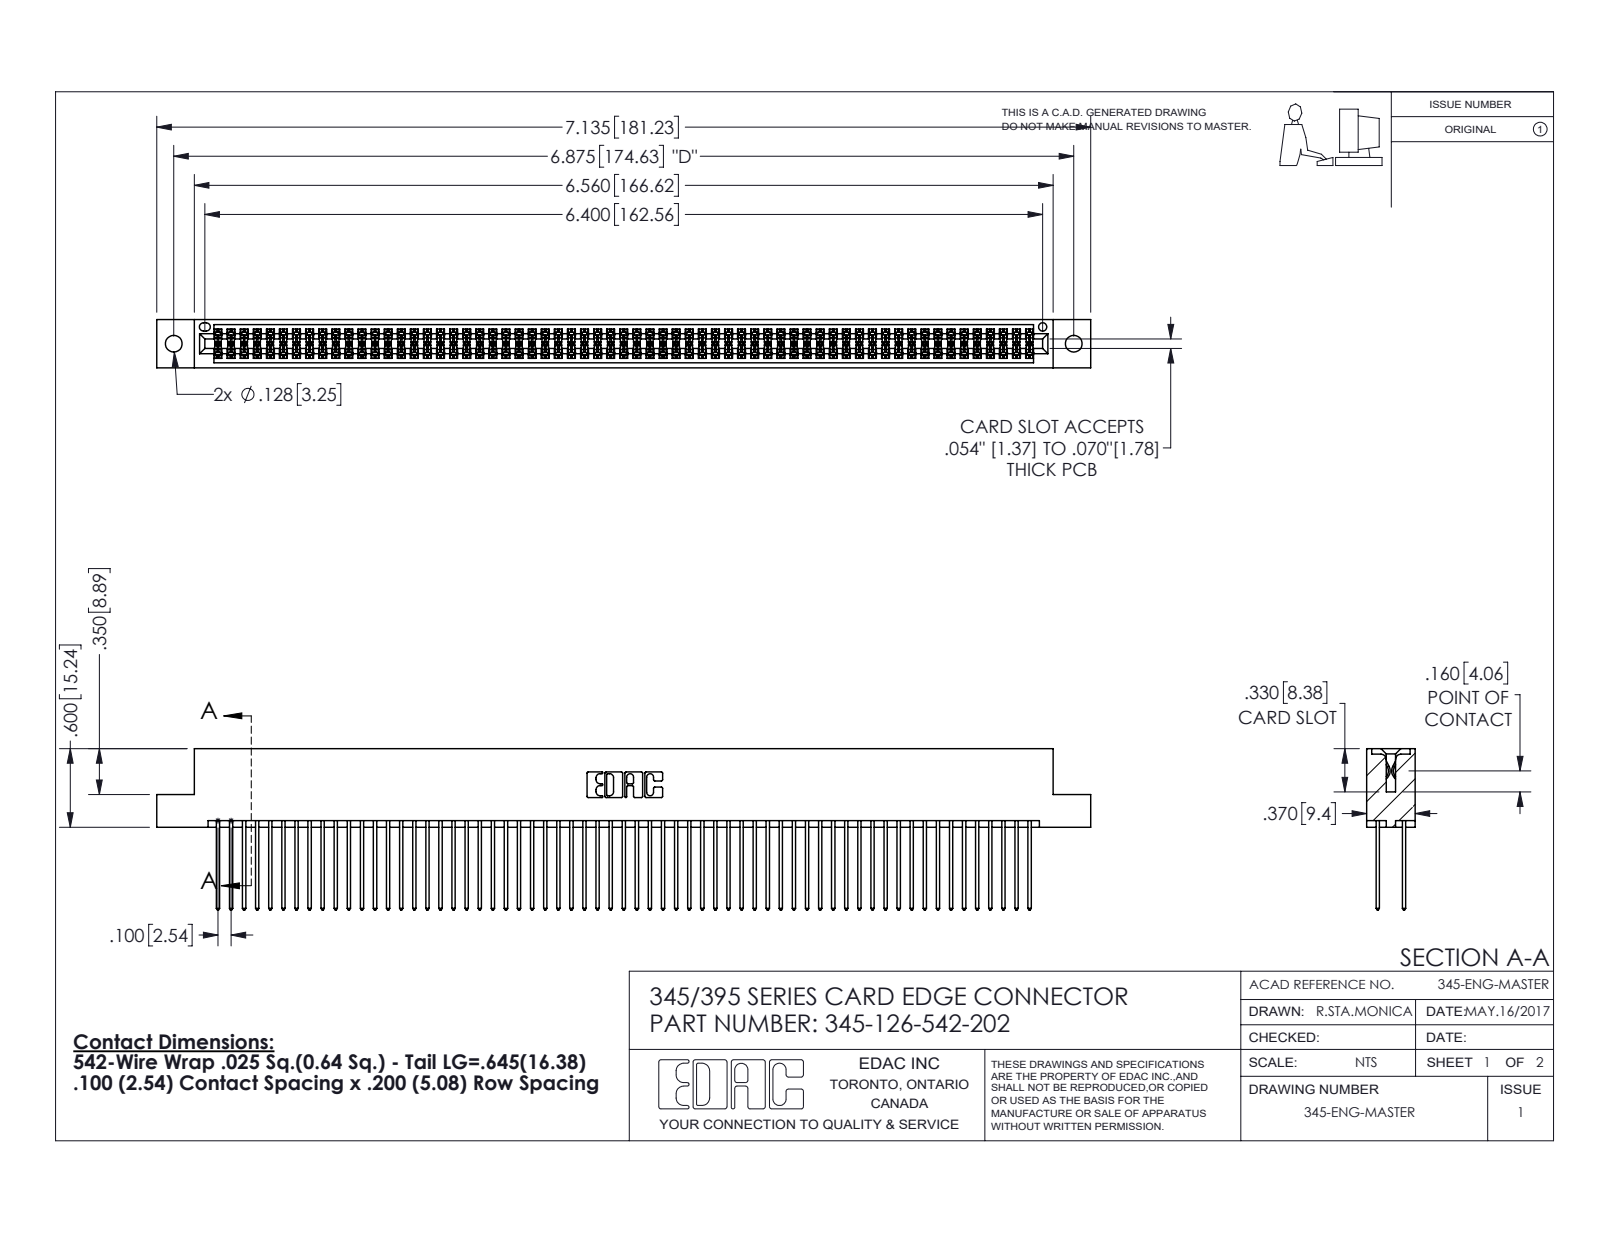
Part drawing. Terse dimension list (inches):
name: 345-126-542-202; 345-292-001_345-293-142; 345 Part_Flush Mounting Lugs - 0.128 Dia
written by: SolidWorks 2016 (CONFIG_CONTROL_DESIGN)
unit: in
bodies: 127 solids, 6426 faces (4238 planar, 2188 cylindrical, 0 other)
size: 7.135 × 1.232 × 0.37
volume: 1.12 in³; area: 46.51 in²
holes: 2× ⌀0.128, 1× ⌀0.064
rounds: 189× R0.006, 126× R0.01, 22× R0.01, 6× R0.007, 6× R0.031, 3× R0.026, 2× R0.014, 2× R0.019
face distances: 0.298, 0.072, 0.2, 0.098, 0.272, 0.025, 0.225, 0.37, 0.175, 0.149
hole spacings: 0.27, 6.639, 6.875
